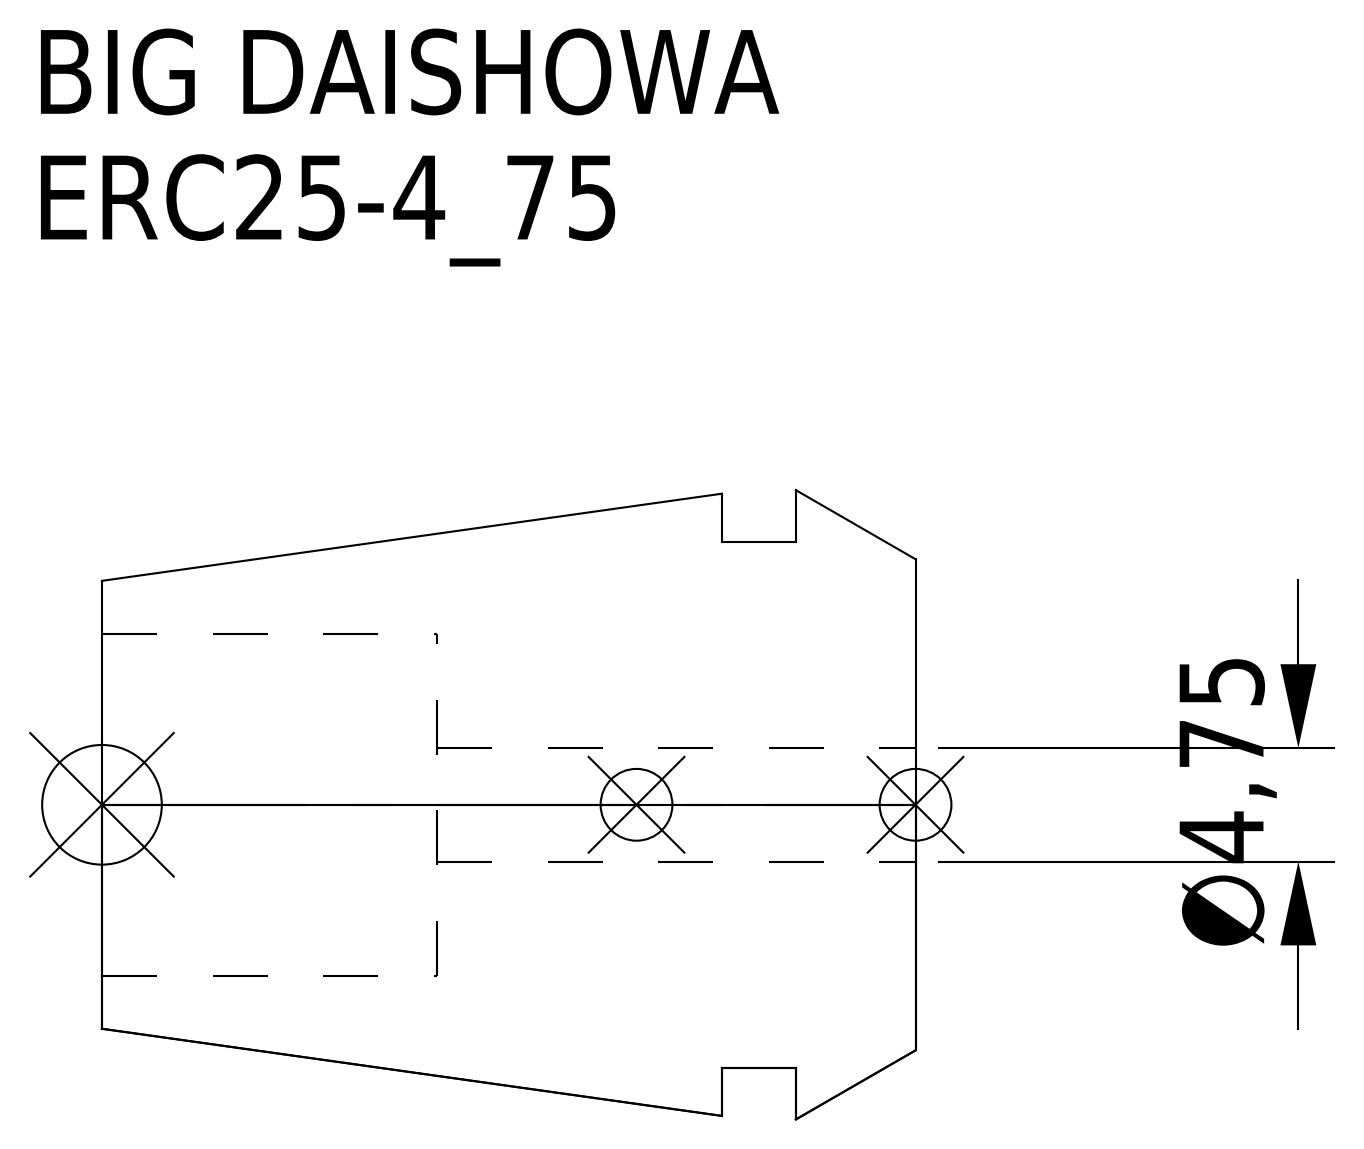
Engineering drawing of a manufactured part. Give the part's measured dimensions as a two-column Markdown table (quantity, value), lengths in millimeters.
| quantity | value |
| --- | --- |
| part name | ERC25-4_75 |
| STEP written by | CREO PARAMETRIC BY PTC INC, 2016380 (AUTOMOTIVE_DESIGN) |
| units | millimeters |
| bodies | 1 solid, 15 faces (5 planar, 6 cylindrical, 4 other) |
| overall size | 34 × 26.3 × 26.3 |
| volume | 11 000 mm³ |
| surface area | 4 288 mm² |
| round holes (diameter × count) | 4.75 × 1, 14.3 × 1 |
| round bosses / shafts (diameter × count) | 22 × 1 |
| main face-to-face distances | 5, 8.1, 3.1, 20, 15, 11.9, 34, 29, 25.9, 14 |
